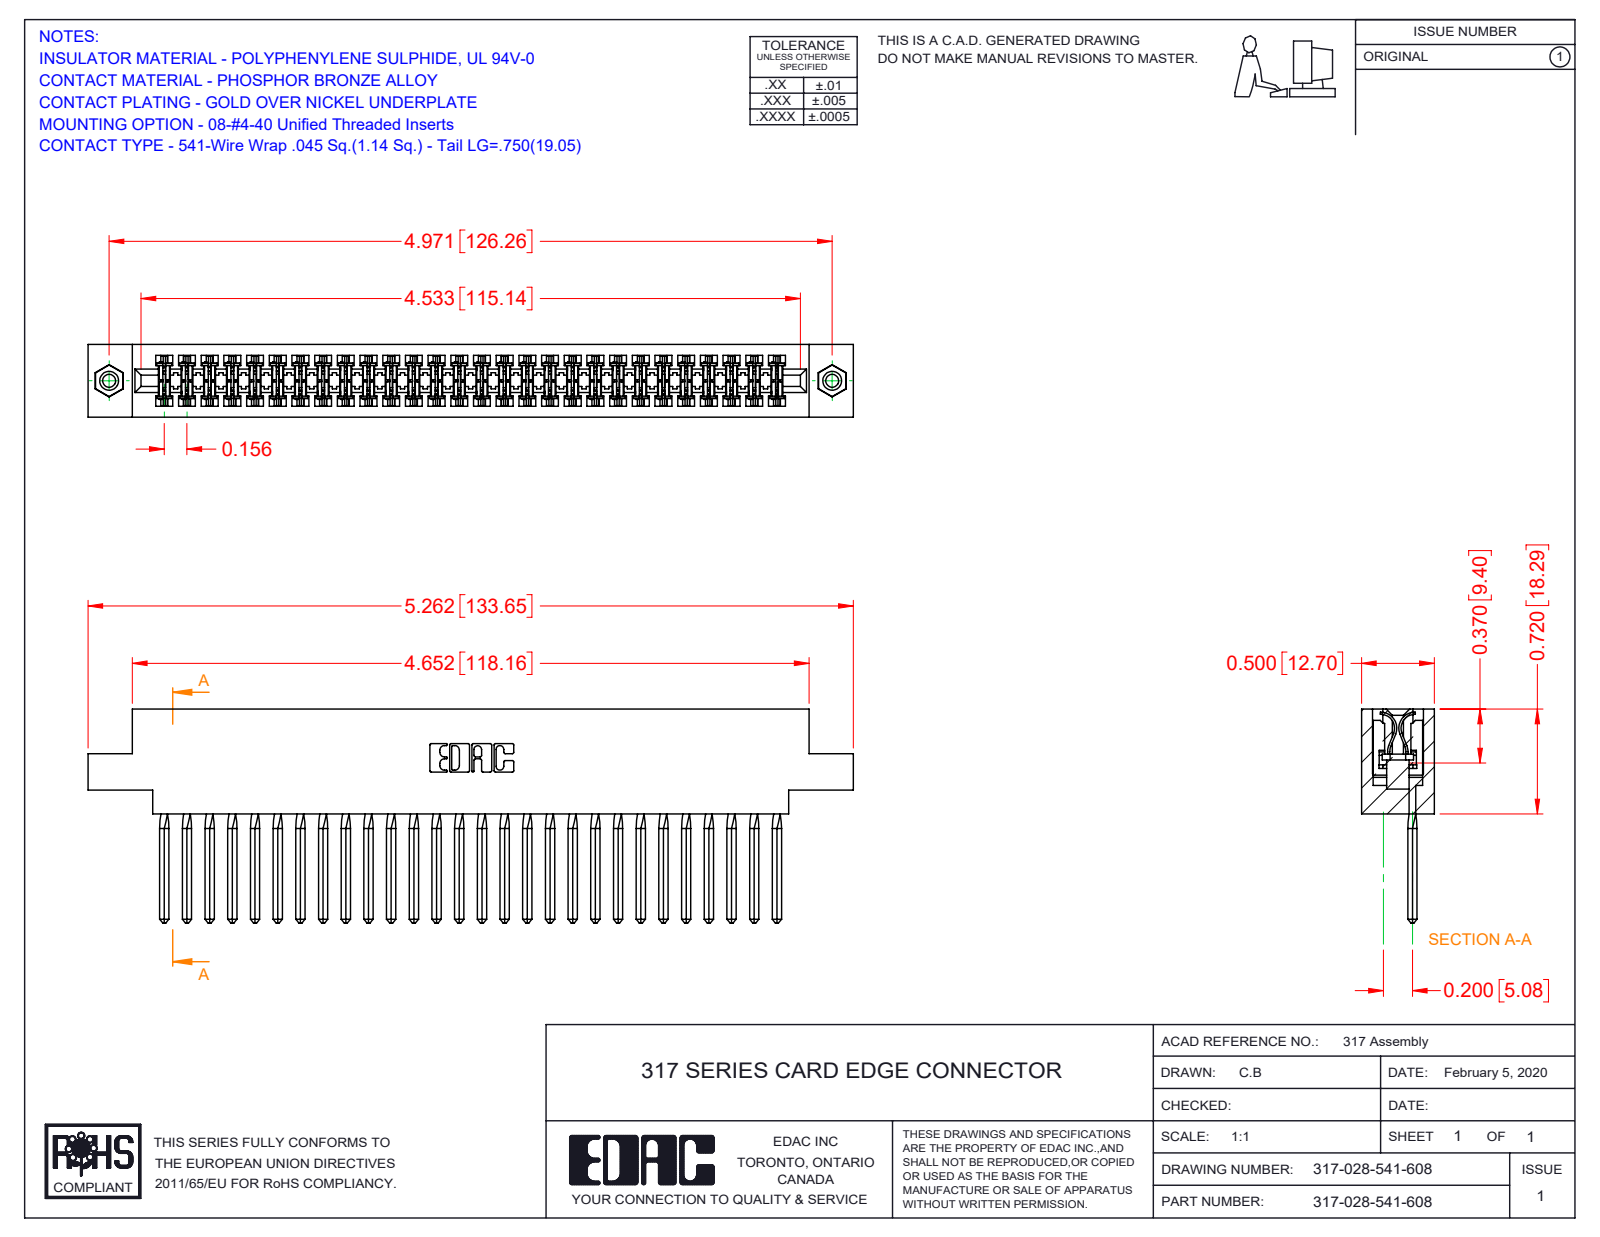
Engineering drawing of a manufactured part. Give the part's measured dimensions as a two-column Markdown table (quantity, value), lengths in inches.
| quantity | value |
| --- | --- |
| part name | 317-028-541-608; 317-290-002_541; 345-250-001_345-250-003-102; 317 Part_.156 Dia - TI |
| STEP written by | SolidWorks 2016 (CONFIG_CONTROL_DESIGN) |
| units | inches |
| bodies | 31 solids, 4418 faces (3562 planar, 728 cylindrical, 128 other) |
| overall size | 5.262 × 1.47 × 0.5 |
| volume | 1.296 in³ |
| surface area | 45.83 in² |
| round holes (diameter × count) | 0.089 × 2, 0.125 × 2, 0.156 × 2 |
| round bosses / shafts (diameter × count) | 0.155 × 2 |
| partial cylindrical surfaces (radius × count) | 0.015 × 56, 0.01 × 22, 0.007 × 6, 0.031 × 6, 0.026 × 3, 0.095 × 2, 0.1 × 2, 0.11 × 2 |
| main face-to-face distances | 0.5, 0.075, 0.425, 0.35, 0.11, 0.195, 0.72, 0.136, 0.115, 0.211 |
| hole center spacings | 4.971 |
